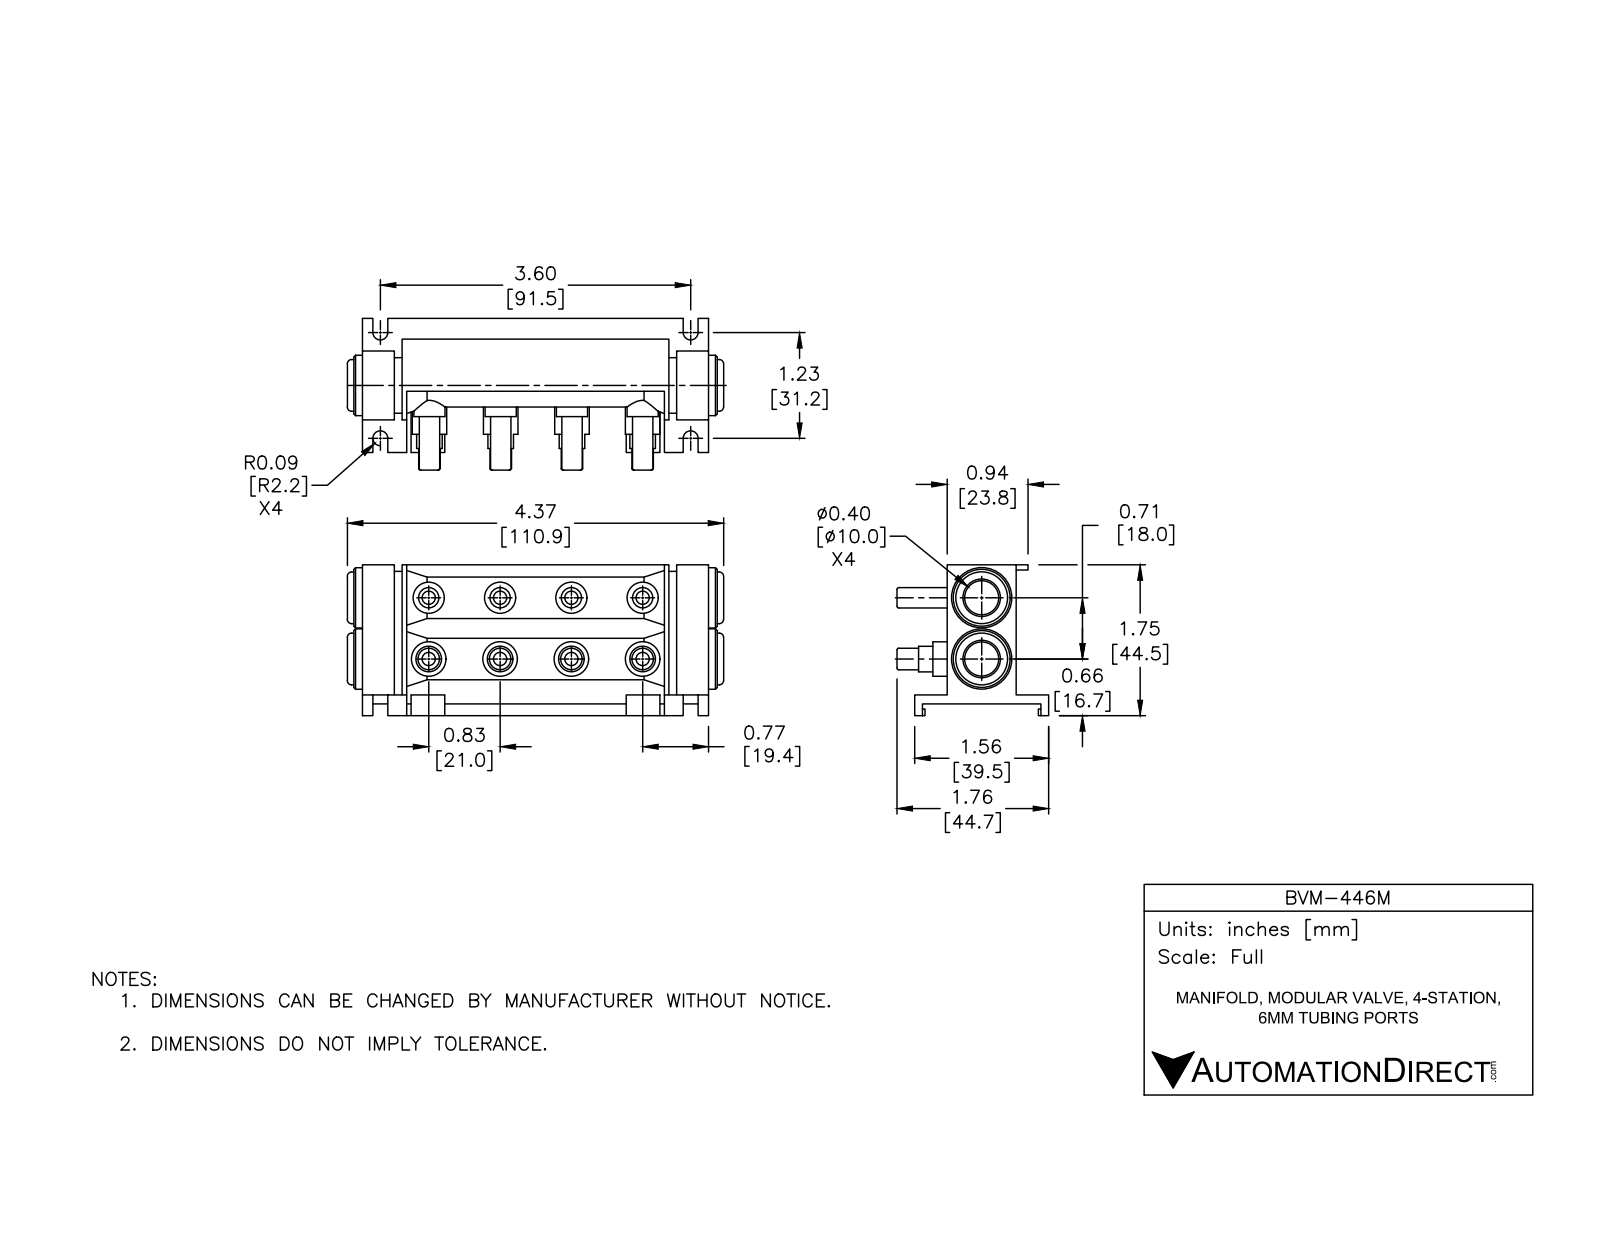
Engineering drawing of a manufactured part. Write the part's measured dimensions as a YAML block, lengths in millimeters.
part_name: "BVM-446M"
step_written_by: "SolidWorks 2016 (AUTOMOTIVE_DESIGN)"
units: millimeters
bodies: {solids: 5, faces: 320, planar: 144, cylindrical: 128, other: 48}
overall_size: [110.2, 44.7, 44.5]
volume: 47030
surface_area: 37060
round_holes:
  - {diameter: 2.6, count: 8}
  - {diameter: 3.9, count: 6}
  - {diameter: 3.9, count: 2}
  - {diameter: 9.9, count: 2}
round_bosses_or_shafts:
  - {diameter: 6, count: 8}
  - {diameter: 10.2, count: 4}
  - {diameter: 9.2, count: 4}
  - {diameter: 7.5, count: 4}
  - {diameter: 17.8, count: 2}
  - {diameter: 15.2, count: 2}
  - {diameter: 12.7, count: 2}
partial_cylinders:
  - {radius: 2.2, count: 4}
face_to_face_distances: [2.6, 8.4, 11.9, 41, 38.4, 101.3, 1.5, 39.4, 36.8, 20.3]
hole_center_spacings: [18, 21, 27.7, 21, 27.7, 42, 42, 45.7]
